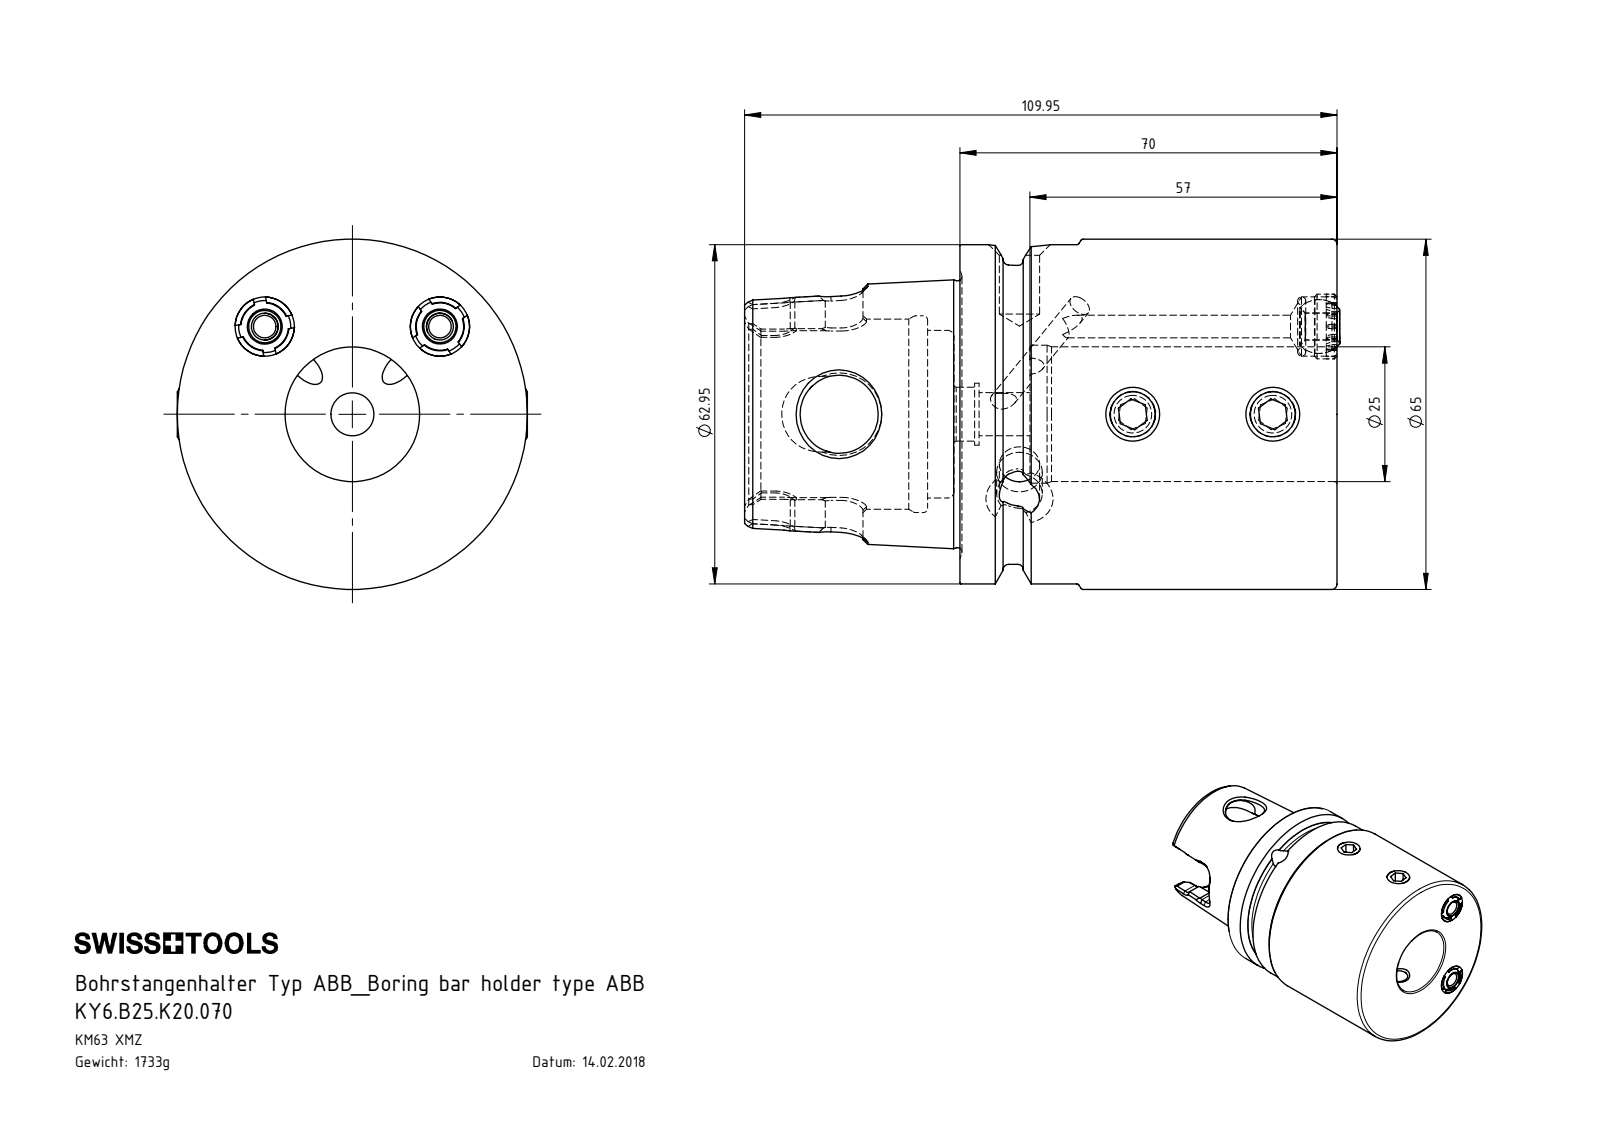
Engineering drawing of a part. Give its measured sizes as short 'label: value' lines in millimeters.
name: KY6-B25.K20.070; KU1-U12.002.010; KU1-U12.002.010_A; KU1-U12.003.010_A (+2 more)
written by: SolidWorks 2012 (CONFIG_CONTROL_DESIGN)
unit: mm
bodies: 9 solids, 394 faces (119 planar, 110 cylindrical, 165 other)
size: 113.52 × 65 × 65
volume: 219 375 mm³; area: 44 788 mm²
holes: 4× ⌀6, 3× ⌀10, 2× ⌀5, 2× ⌀7.47, 2× ⌀8.5, 2× ⌀11, 1× ⌀8, 1× ⌀8.48, 1× ⌀11.5, 1× ⌀14.5, 1× ⌀25, 1× ⌀25.6
bosses: 2× ⌀12, 2× ⌀10, 1× ⌀65, 1× ⌀62.95, 1× ⌀55.7
rounds: 6× R4, 2× R4.4, 2× R7.04
face distances: 70, 1.1, 71.1, 14.1, 13, 57, 6, 4.9, 19, 76
hole spacings: 23, 26, 32.1, 32.52, 54.5, 80.5
